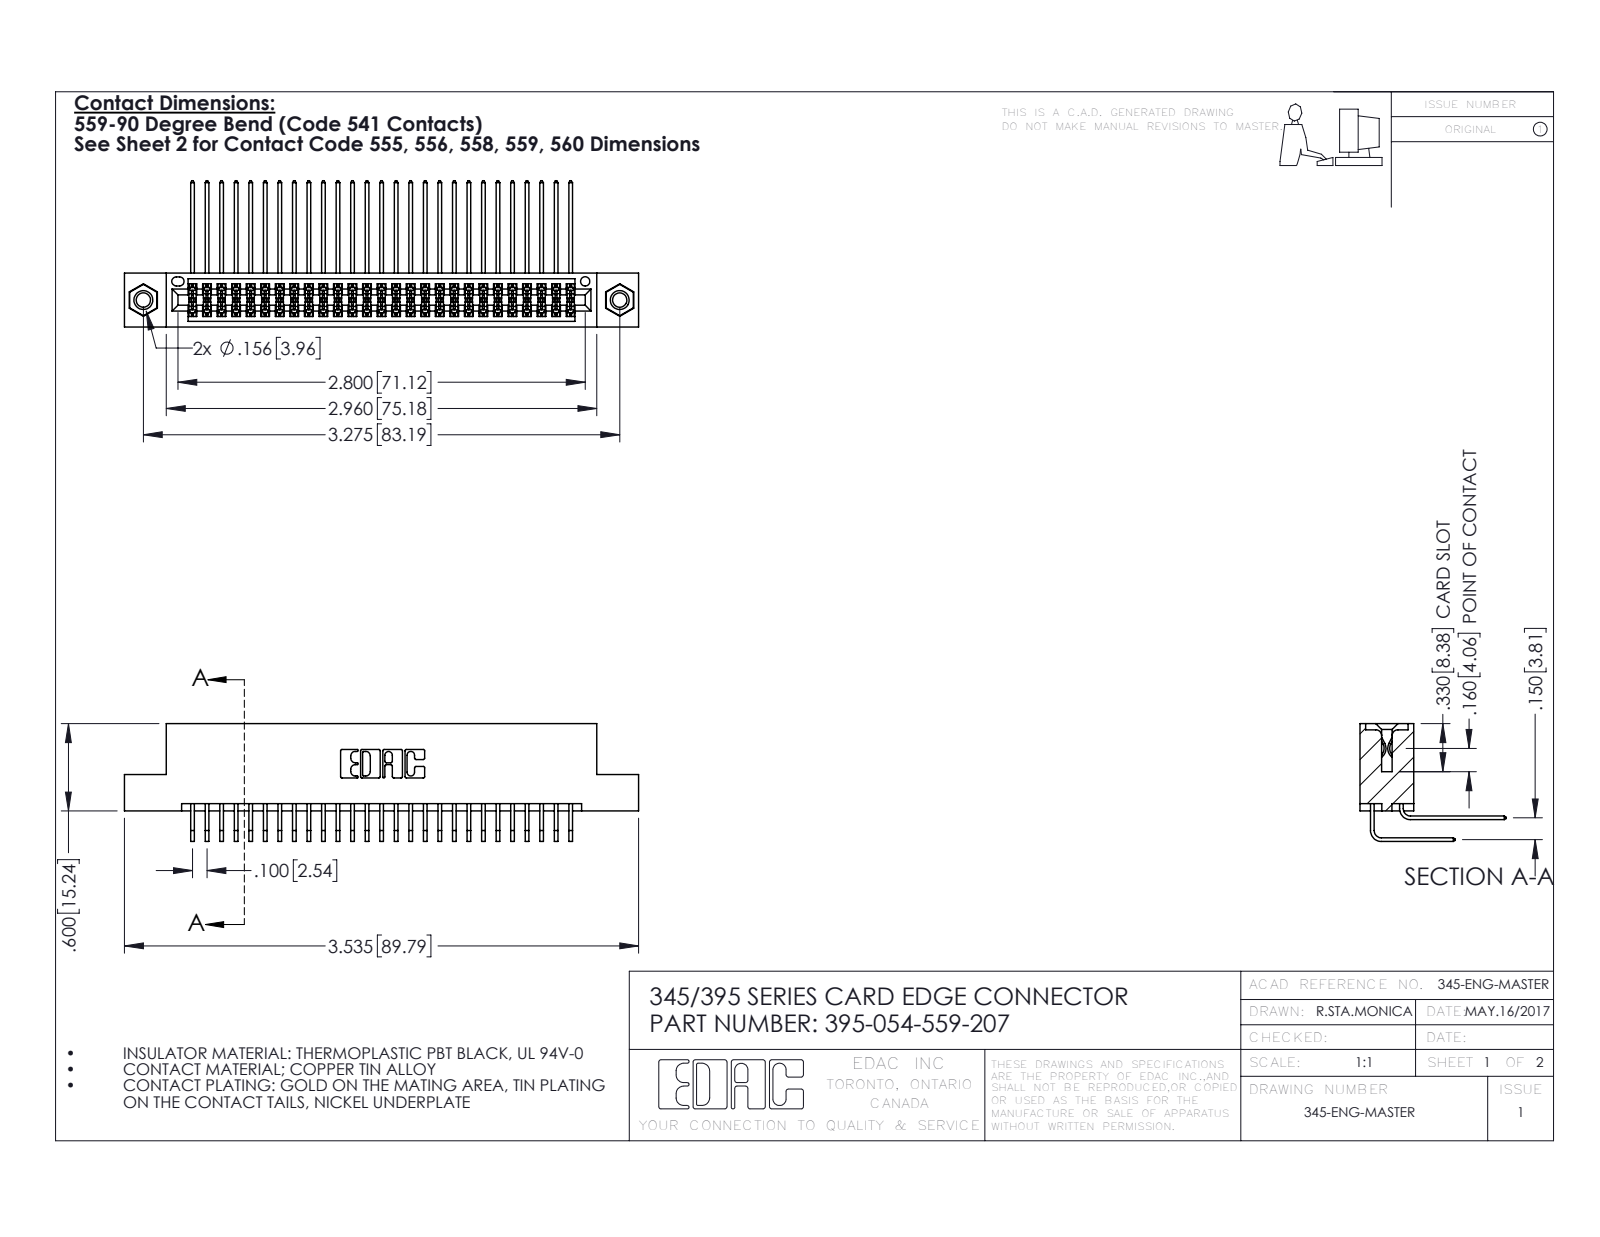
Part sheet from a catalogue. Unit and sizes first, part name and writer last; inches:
Units: inches
Overall size (bounding box): 3.535 × 1.005 × 0.809
Round holes (diameter × count): ⌀0.098 ×2, ⌀0.125 ×2, ⌀0.156 ×2, ⌀0.064 ×1
Round bosses / shafts (diameter × count): ⌀0.155 ×2
Partial cylindrical surfaces — rounded edges, fillets, slot ends (radius × count): R0.006 ×81, R0.01 ×22, R0.007 ×6, R0.031 ×6, R0.026 ×3, R0.014 ×2, R0.019 ×2, R0.022 ×2
Main face-to-face distances: 0.072, 0.298, 0.2, 0.37, 0.098, 0.272, 0.025, 0.225, 0.15, 0.175
Hole centre spacings: 0.27, 3.04, 3.275
Volume: 0.542 in³ · Surface area: 22.21 in²
Bodies: 57 solids, 2994 faces (2002 planar, 976 cylindrical, 16 other)
Part name (STEP PRODUCT): 345-292-001_558 559 Tail - 1; 395-054-559-207; 345 Part_Flush Mounting Lugs - 0.156 Dia-TI; 345-250-001_345-250-005-103 (+1 more)
STEP written by: SolidWorks 2016 (CONFIG_CONTROL_DESIGN)
